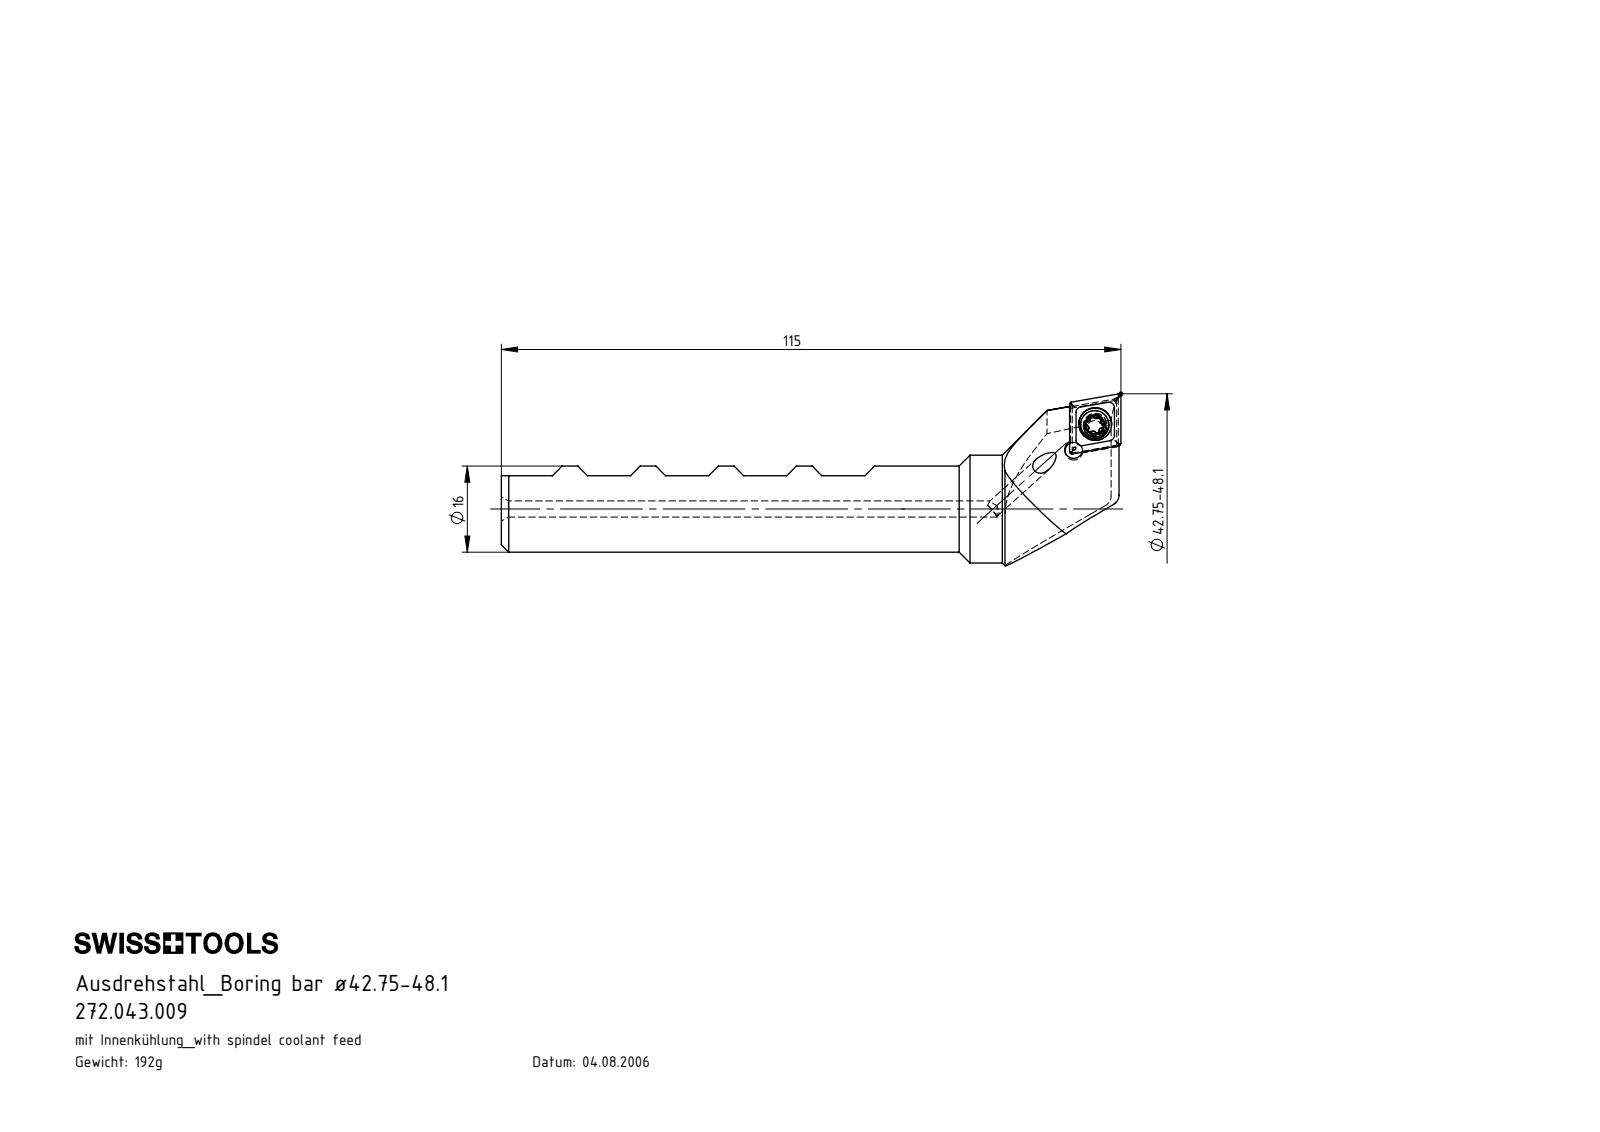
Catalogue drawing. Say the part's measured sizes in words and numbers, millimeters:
The part is named "B43-WCB.K11.115; WCB-ER2.001.009_A; CCMT09T304; B43-WCB.K11.115_A". Its 3-D file was written by "SolidWorks 2012 (CONFIG_CONTROL_DESIGN)". It is 3 solids with 144 faces: 45 planar, 39 cylindrical and 60 other. Overall it measures 115 by 31.88 by 22.48 millimeters. Its volume is 24 414 cubic millimeters and its surface area 8 335 square millimeters. Round holes: 2 of diameter 3, 2 of diameter 3.3, 1 of diameter 4.4, 1 of diameter 6.1. Round bosses or shafts: 1 of diameter 20, 1 of diameter 16, 1 of diameter 5.25, 1 of diameter 4. Partial cylindrical surfaces (rounded edges, fillets, slot ends): 6 of radius 0.34, 6 of radius 0.59, 1 of radius 2, 1 of radius 10.5, 1 of radius 12. The main face-to-face distances are 8.39, 10.25, 12.16, 3.77, 20.5, 20.51, 30.76, 12.36, 3.97, 30.75. The hole center spacings are 6.07, 6.2.
